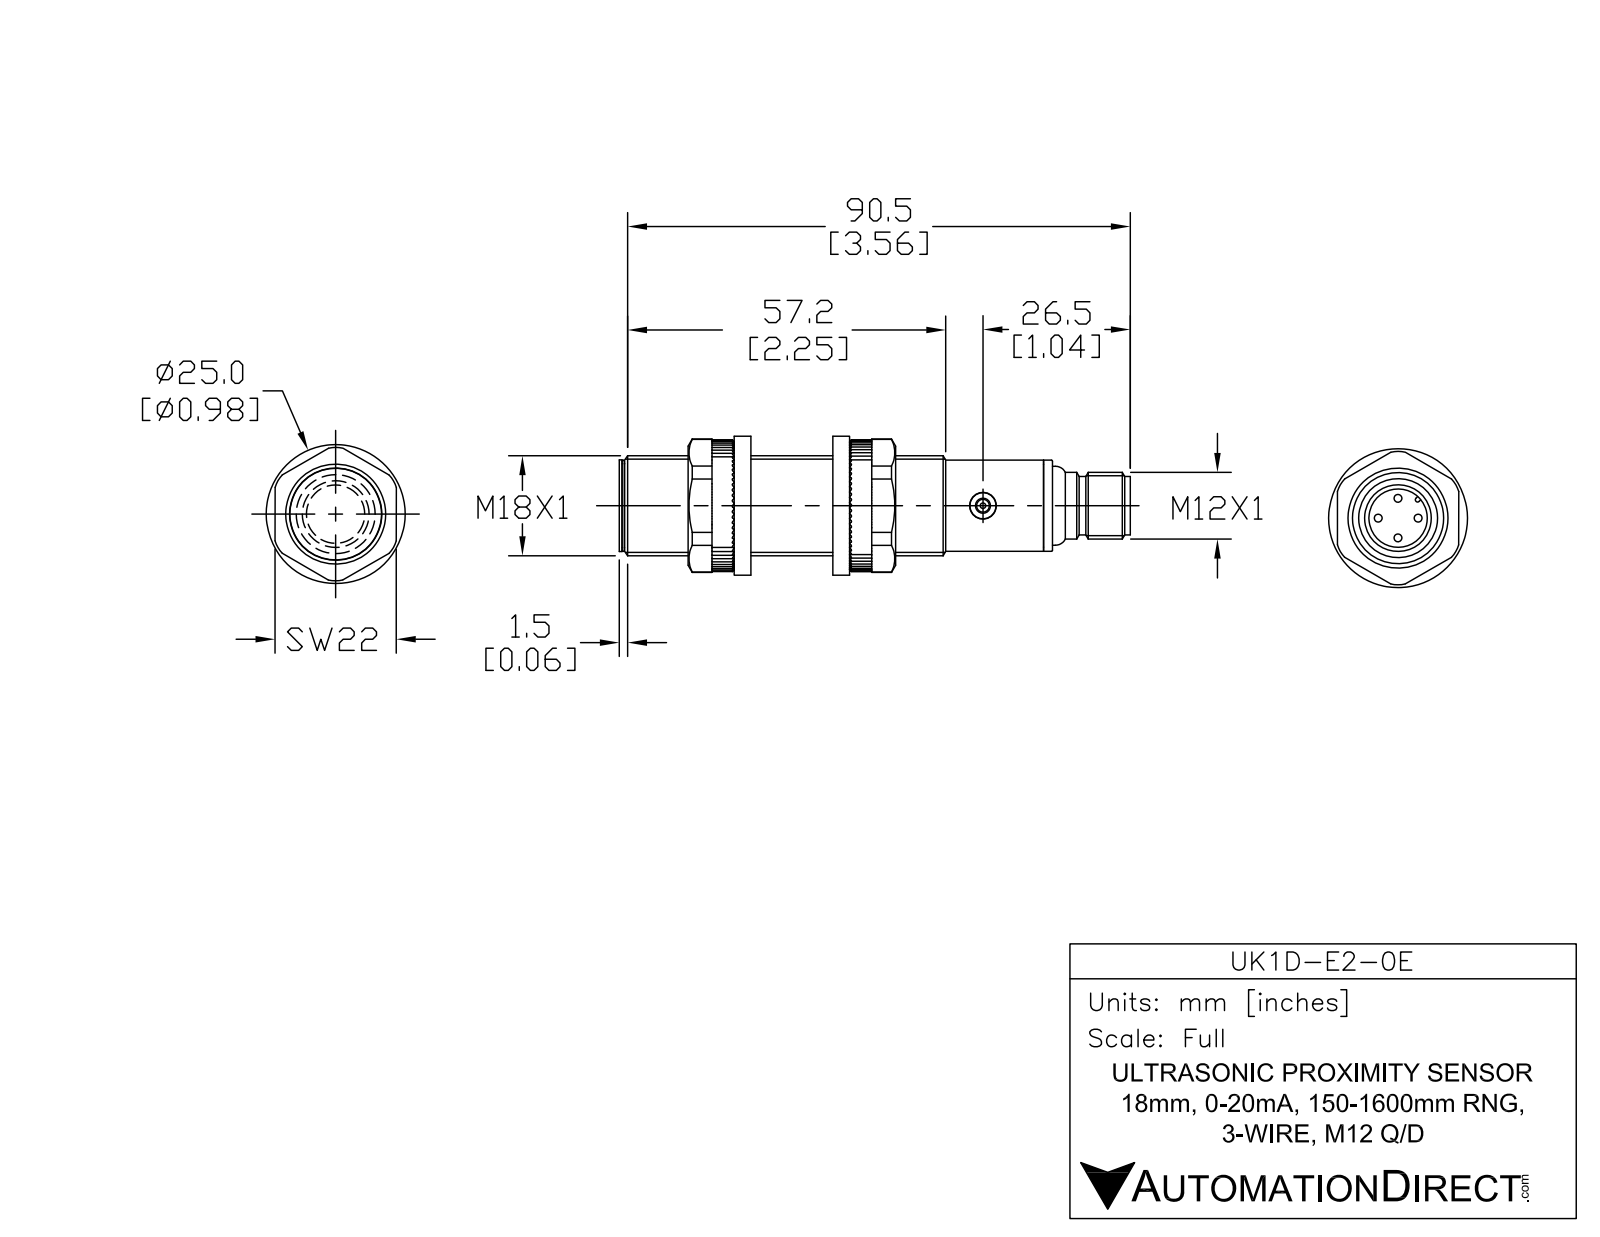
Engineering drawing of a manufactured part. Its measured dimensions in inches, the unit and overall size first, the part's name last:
Units: inches
Overall size (bounding box): 3.606 × 0.709 × 0.709
Round holes (diameter × count): ⌀0.106 ×1, ⌀0.185 ×1, ⌀0.276 ×1, ⌀0.327 ×1, ⌀0.374 ×1
Round bosses / shafts (diameter × count): ⌀0.039 ×4, ⌀0.709 ×1, ⌀0.654 ×1, ⌀0.646 ×1, ⌀0.622 ×1, ⌀0.559 ×1, ⌀0.472 ×1, ⌀0.413 ×1
Partial cylindrical surfaces — rounded edges, fillets, slot ends (radius × count): R0.024 ×1
Main face-to-face distances: 2.957, 0.039, 2.996, 0.037, 2.994, 0.043, 0.157, 3.055, 3.053, 3.016
Volume: 1.202 in³ · Surface area: 10.68 in²
Bodies: 6 solids, 106 faces (21 planar, 48 cylindrical, 37 other)
Part name (STEP PRODUCT): UK1D-E2-0E
STEP written by: SolidWorks 2017 (AUTOMOTIVE_DESIGN)
